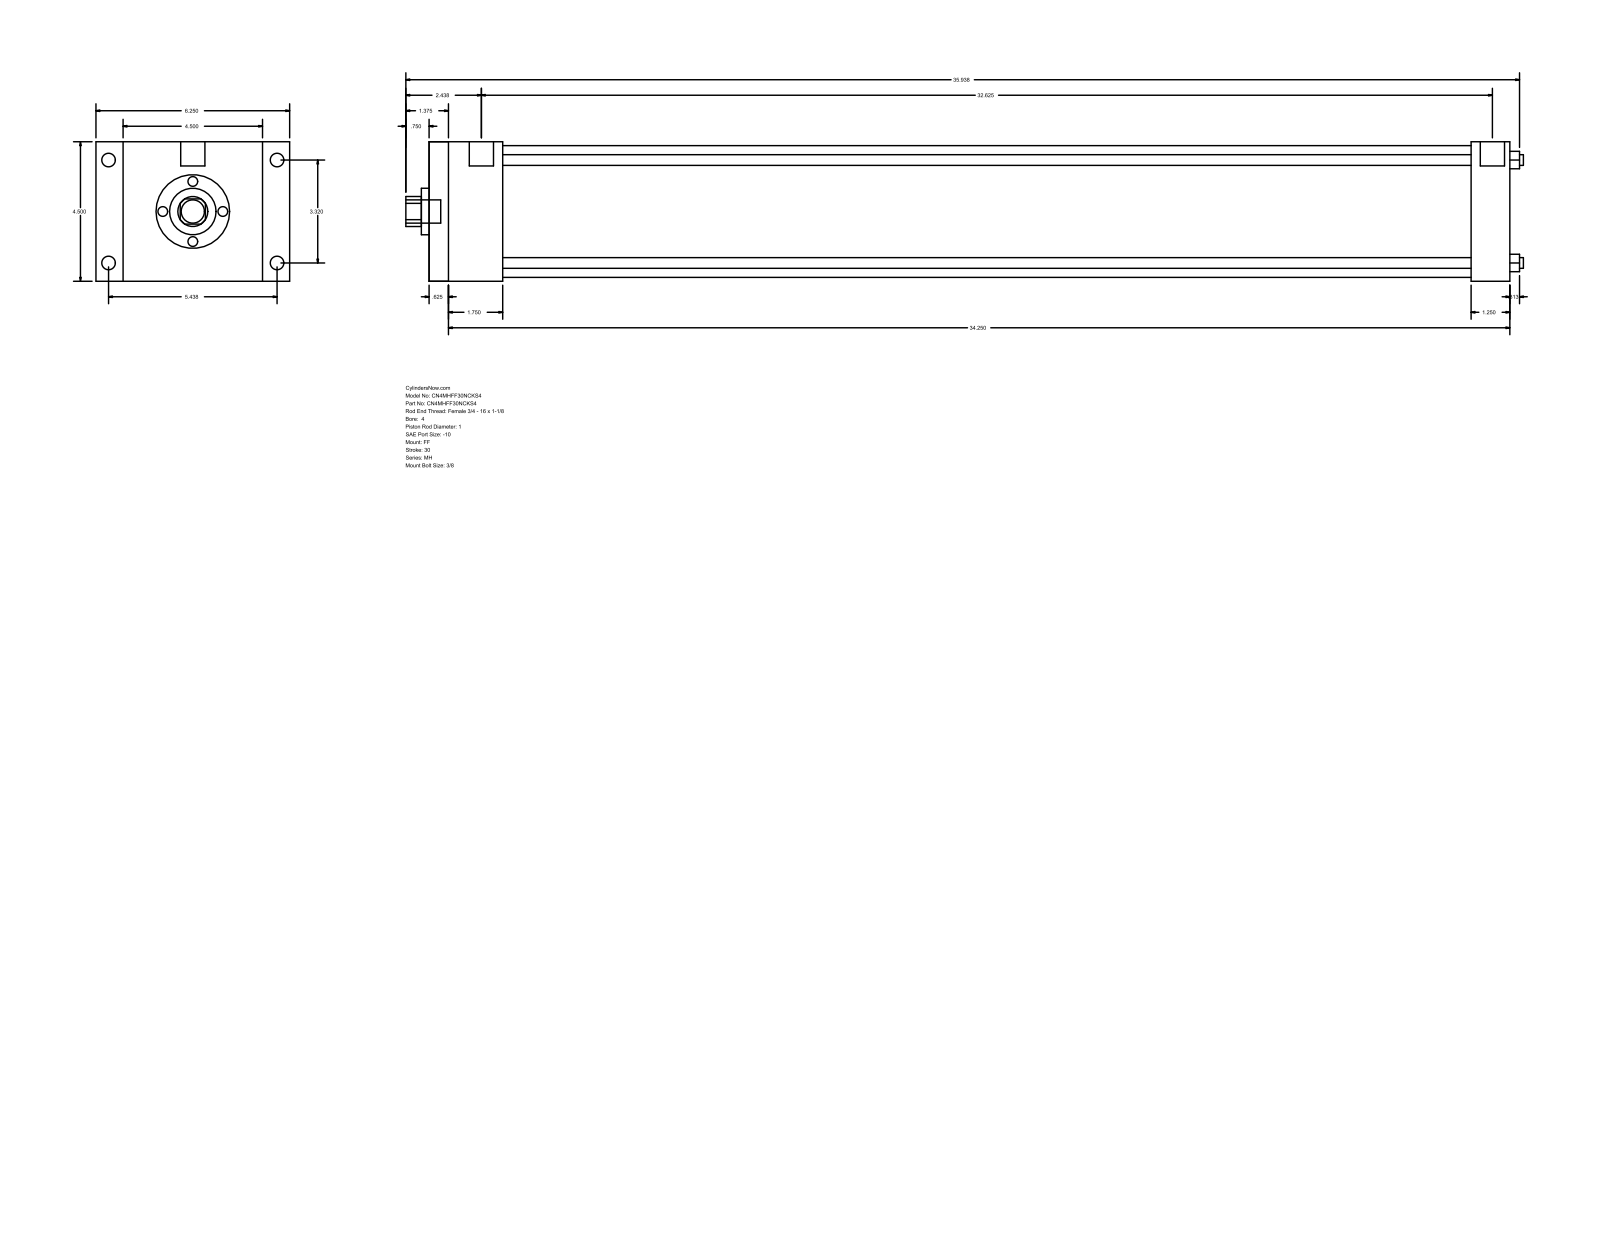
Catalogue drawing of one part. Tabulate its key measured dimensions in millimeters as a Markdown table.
| quantity | value |
| --- | --- |
| part name | MH_FF__0400_1 |
| STEP written by | GSSL Pune (CONFIG_CONTROL_DESIGN) |
| units | millimeters |
| bodies | 0 solids, 92 faces (64 planar, 28 cylindrical, 0 other) |
| overall size | 915.99 × 158.75 × 114.3 |
| round holes (diameter × count) | 8.76 × 4, 25.4 × 1, 38.1 × 1, 107.95 × 1 |
| round bosses / shafts (diameter × count) | 11.13 × 4, 8.73 × 4, 19.84 × 2, 19.05 × 1 |
| partial cylindrical surfaces (radius × count) | 12.29 × 1 |
| main face-to-face distances | 114.3, 885.83, 15.87, 869.96, 60.33, 44.46, 825.5, 854.07, 838.2, 793.74 |
| hole center spacings | 59.62, 84.32, 119.25 |
